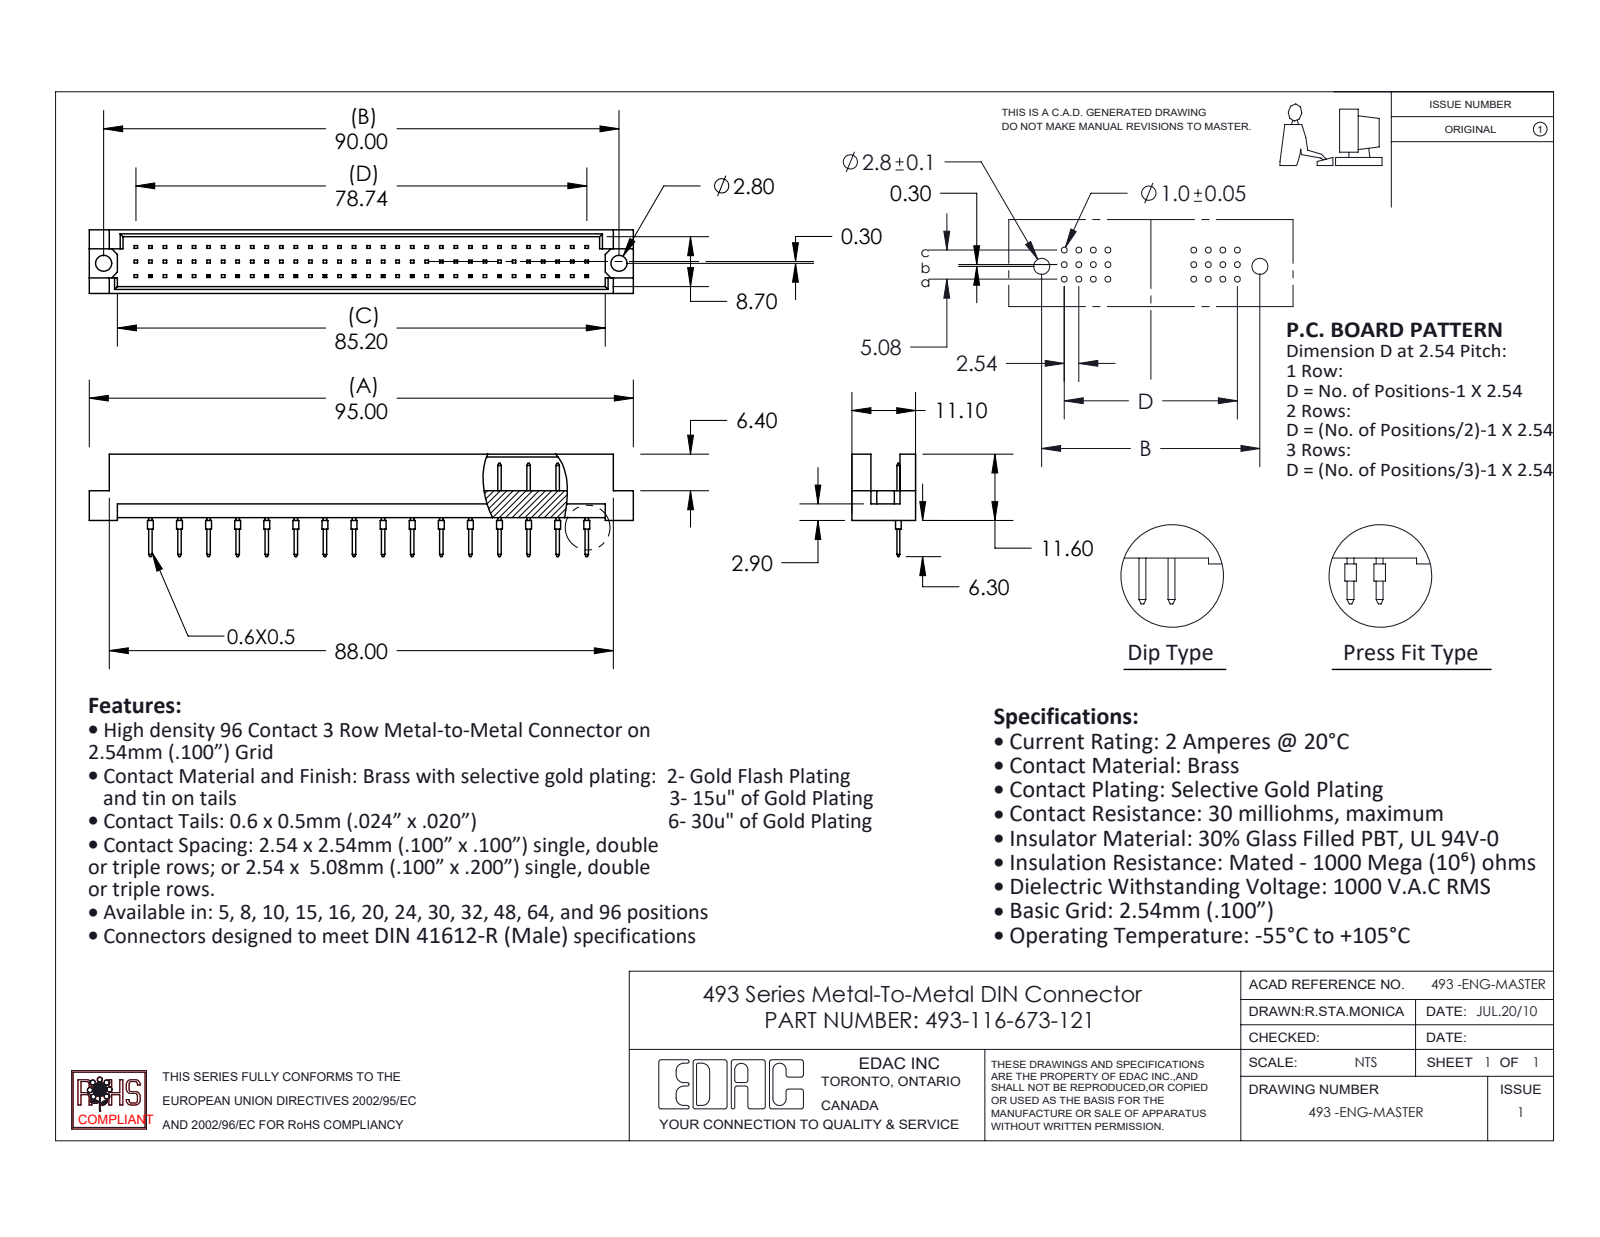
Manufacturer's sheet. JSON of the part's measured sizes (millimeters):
{"part_name": "493-290_73; 493-116-673-121; 493 Part_96", "step_written_by": "SolidWorks 2020 (CONFIG_CONTROL_DESIGN)", "units": "millimeters", "bodies": {"solids": 17, "faces": 788, "planar": 752, "cylindrical": 36, "other": 0}, "overall_size": [95, 17.9, 11.1], "volume_mm3": 5747, "surface_area_mm2": 7080, "round_holes": [[2.8, 2]], "round_bosses_or_shafts": [[1, 16]], "face_to_face_distances": [1.2, 9.9, 11.1, 8.7, 4.7, 0.5, 5.08, 2.54, 2.76, 3.26], "hole_center_spacings": [90]}
